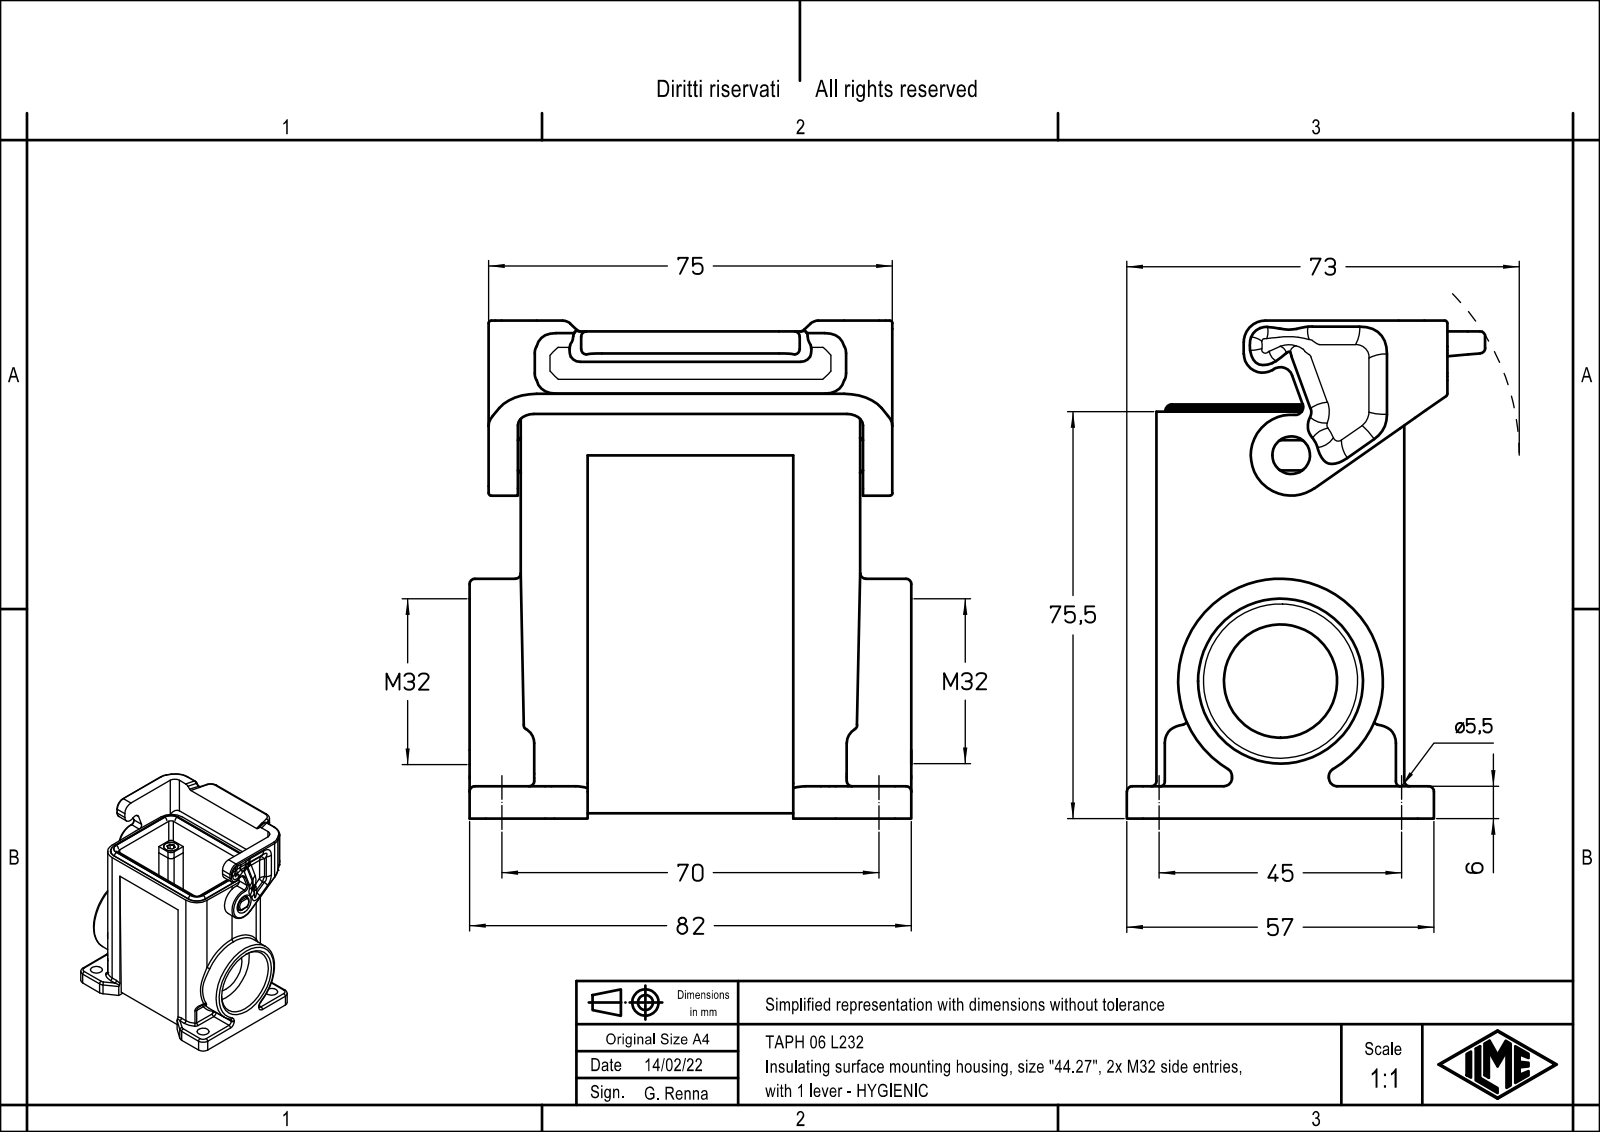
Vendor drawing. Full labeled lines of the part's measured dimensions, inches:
Part name (STEP PRODUCT): TAPH 06 L232
STEP written by: Creo Elements/Direct Modeling 20.1B 02-Apr-2019 (C) Parametric Technology GmbH (AUTOMOTIVE_DESIGN)
Units: inches
Bodies: 1 solid, 325 faces (161 planar, 128 cylindrical, 36 other)
Overall size (bounding box): 3.638 × 3.228 × 2.618
Volume: 7.574 in³ · Surface area: 72.72 in²
Round holes (diameter × count): ⌀0.217 ×4, ⌀1.102 ×1, ⌀1.205 ×1
Round bosses / shafts (diameter × count): ⌀1.496 ×1
Partial cylindrical surfaces — rounded edges, fillets, slot ends (radius × count): R0.118 ×17, R0.079 ×10, R0.059 ×9, R0.039 ×8, R0.051 ×8, R0.02 ×4, R0.236 ×4, R0.276 ×4
Main face-to-face distances: 1.811, 0.213, 1.598, 1.598, 1.385, 0.213, 0.217, 0.039, 0.587, 2.287
Hole centre spacings: 1.772, 2.756, 3.276
